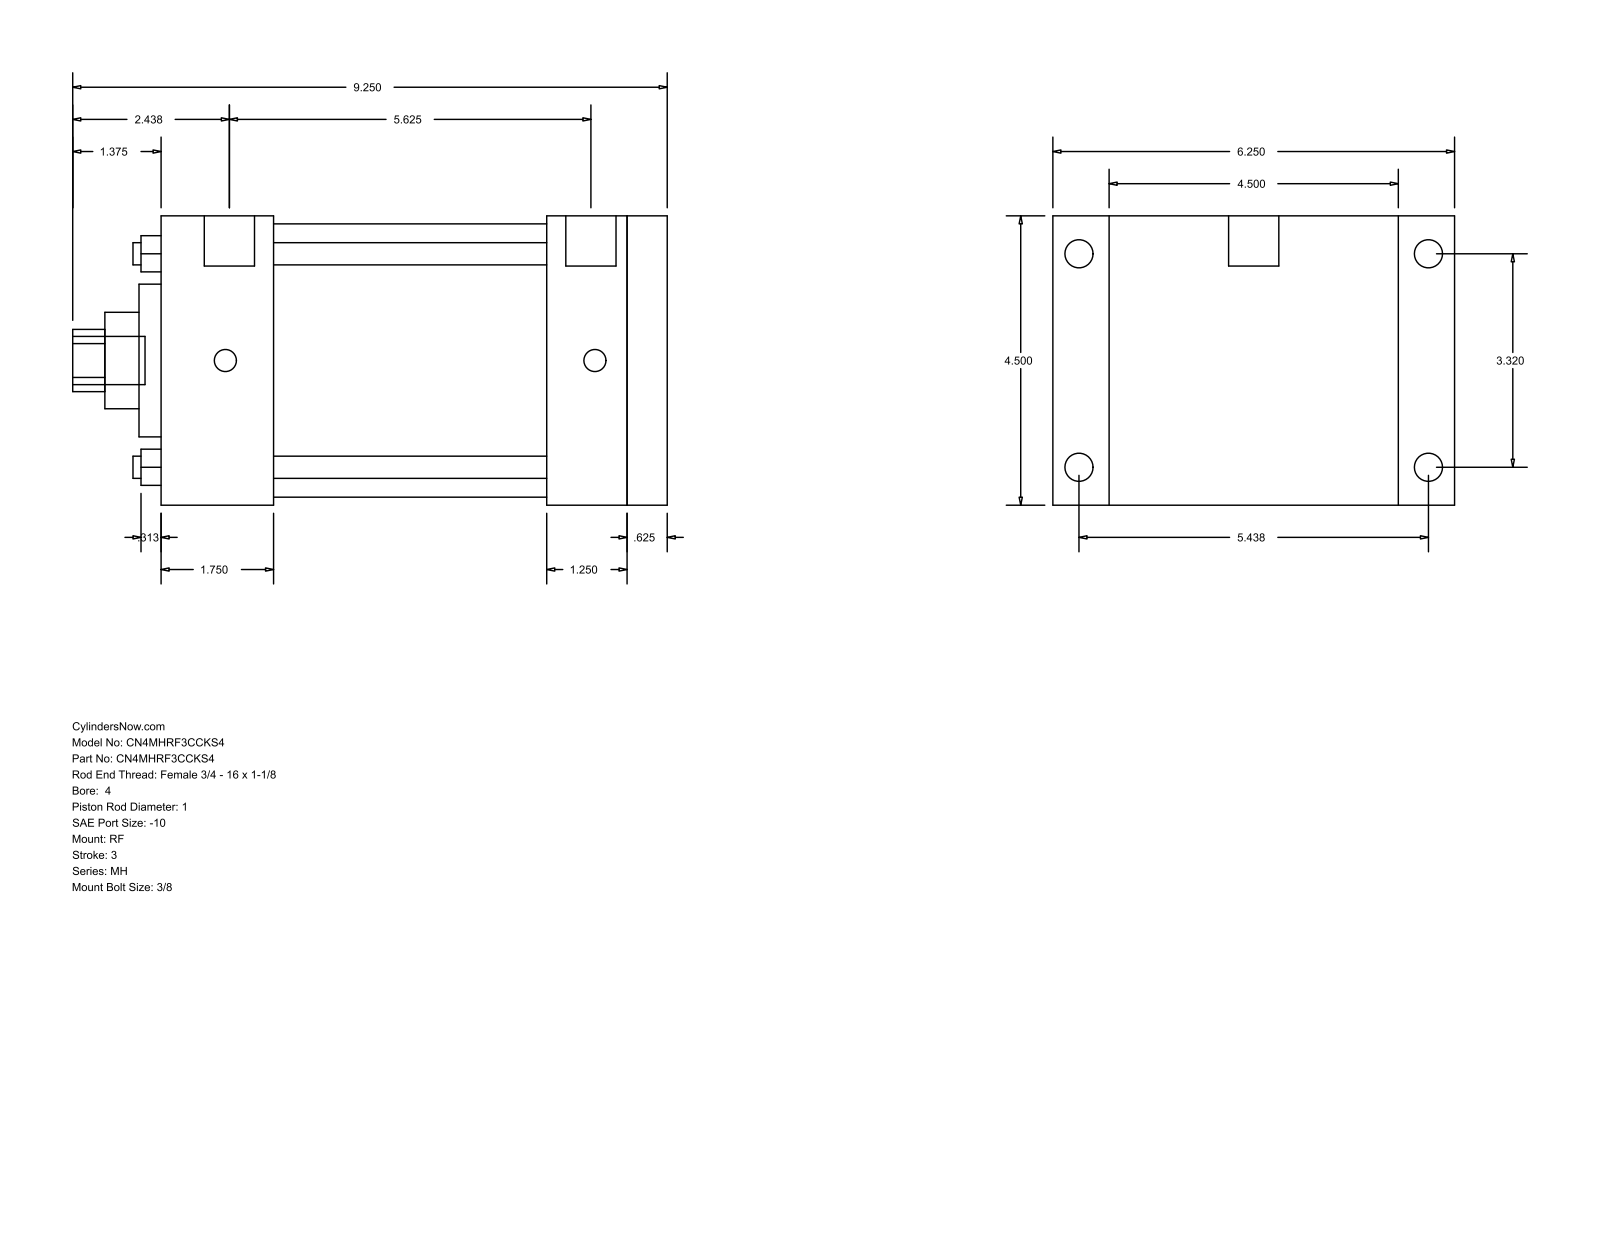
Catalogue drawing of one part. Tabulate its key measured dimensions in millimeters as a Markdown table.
| quantity | value |
| --- | --- |
| part name | MH_RF__0400_1 |
| STEP written by | GSSL Pune (CONFIG_CONTROL_DESIGN) |
| units | millimeters |
| bodies | 0 solids, 94 faces (65 planar, 29 cylindrical, 0 other) |
| overall size | 234.95 × 158.75 × 114.3 |
| round holes (diameter × count) | 8.76 × 4, 25.4 × 1, 38.1 × 1, 60.33 × 1, 107.95 × 1 |
| round bosses / shafts (diameter × count) | 11.13 × 4, 8.73 × 4, 19.84 × 2, 19.05 × 1 |
| partial cylindrical surfaces (radius × count) | 12.29 × 1 |
| main face-to-face distances | 114.3, 200.03, 184.15, 15.88, 47.63, 44.46, 139.69, 155.57, 152.4, 107.94 |
| hole center spacings | 59.62, 84.32, 119.25 |
